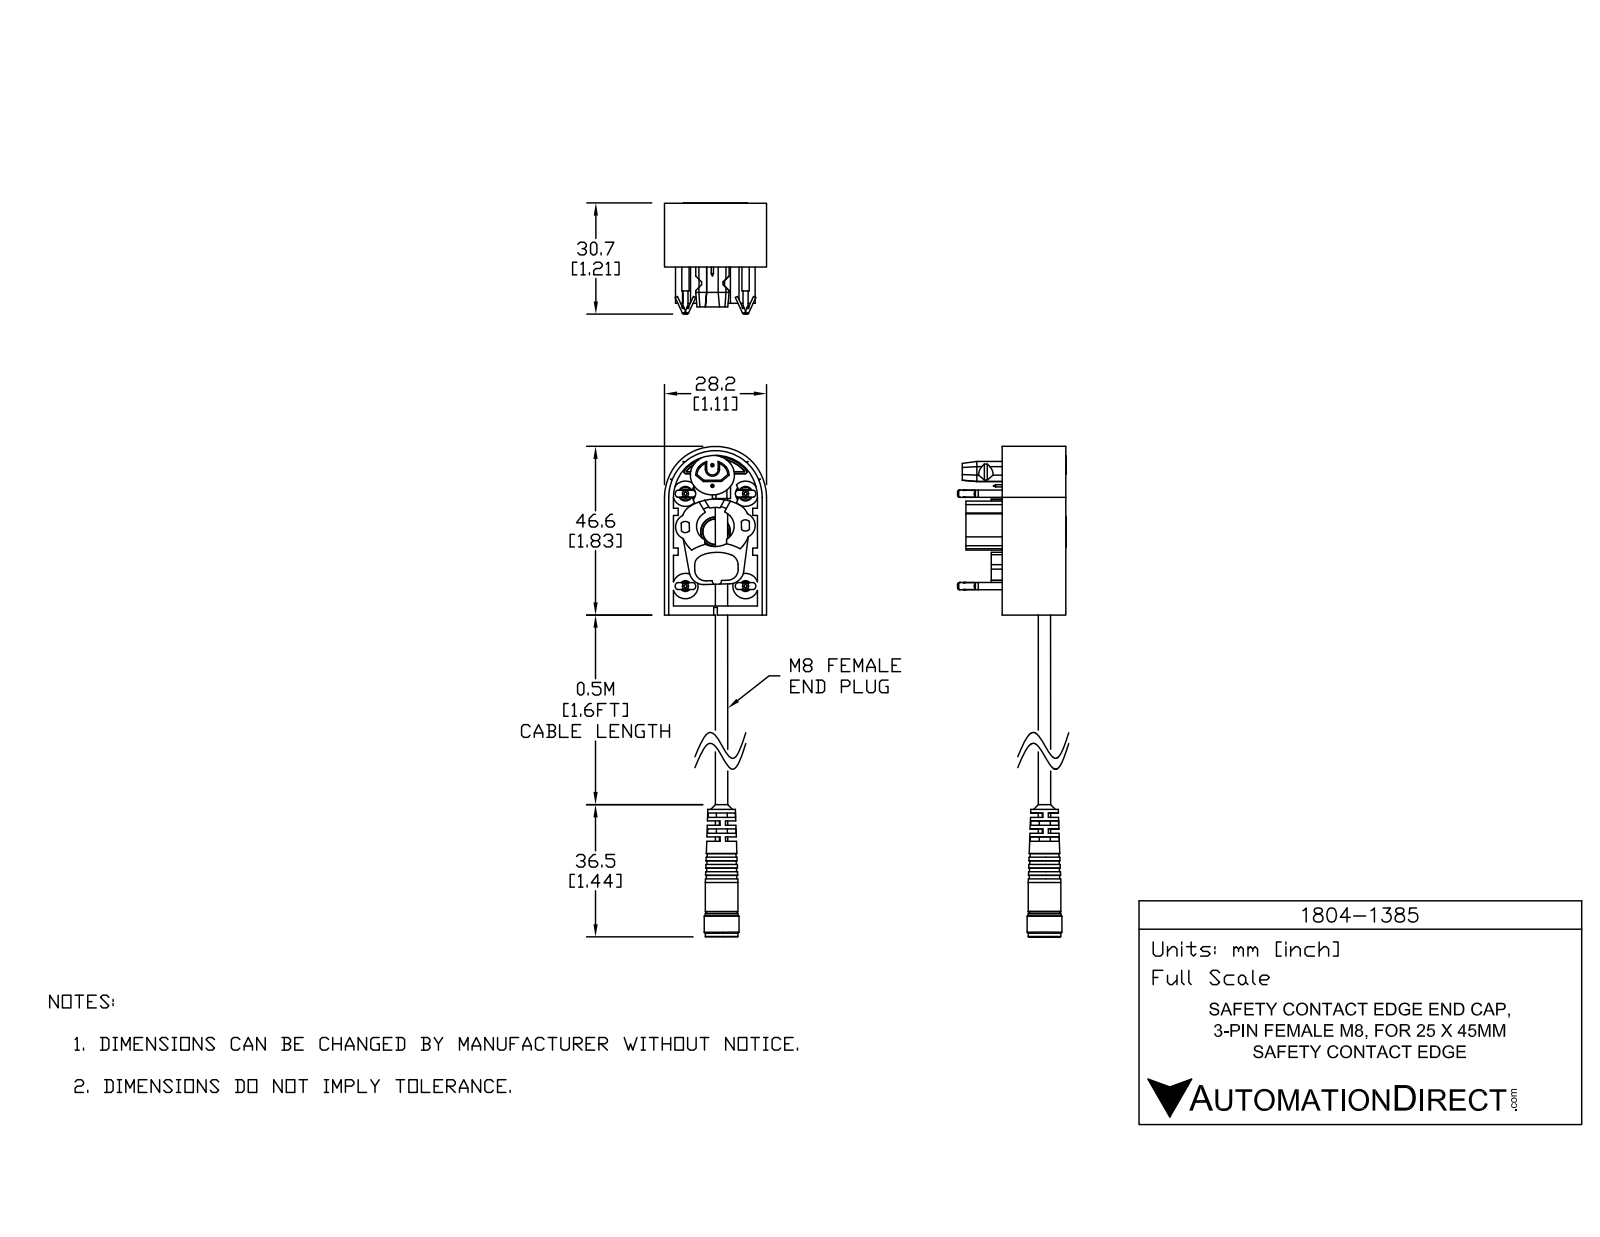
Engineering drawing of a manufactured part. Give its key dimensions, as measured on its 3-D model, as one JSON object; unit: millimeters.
{"part_name": "1804-1385", "step_written_by": "SolidWorks 2021 (AUTOMOTIVE_DESIGN)", "units": "millimeters", "bodies": {"solids": 1, "faces": 513, "planar": 260, "cylindrical": 174, "other": 79}, "overall_size": [135.4, 30, 28.2], "volume_mm3": 14800, "surface_area_mm2": 15570, "round_holes": [[1.5, 5], [0.5, 4], [4, 4], [5.5, 4], [0.9, 2], [3, 2], [3.1, 2], [3.5, 2], [6.9, 2], [5.9, 1], [7.2, 1]], "round_bosses_or_shafts": [[5, 4], [3.5, 4], [2.5, 4], [2, 4], [9, 2], [7, 2], [5.7, 2], [0.7, 2]], "partial_cylinders_radius": [[1, 16], [3, 6], [3.5, 6], [4, 6], [3.9, 4], [5, 4], [4.1, 2], [5.1, 2]], "face_to_face_distances": [2.5, 1.8, 28.2, 1.3, 25.7, 27, 1.2, 24.5, 25.8, 11.6], "hole_center_spacings": [1.8, 16.6, 1.4, 1.8, 2.5, 10.5, 20.7, 23]}
